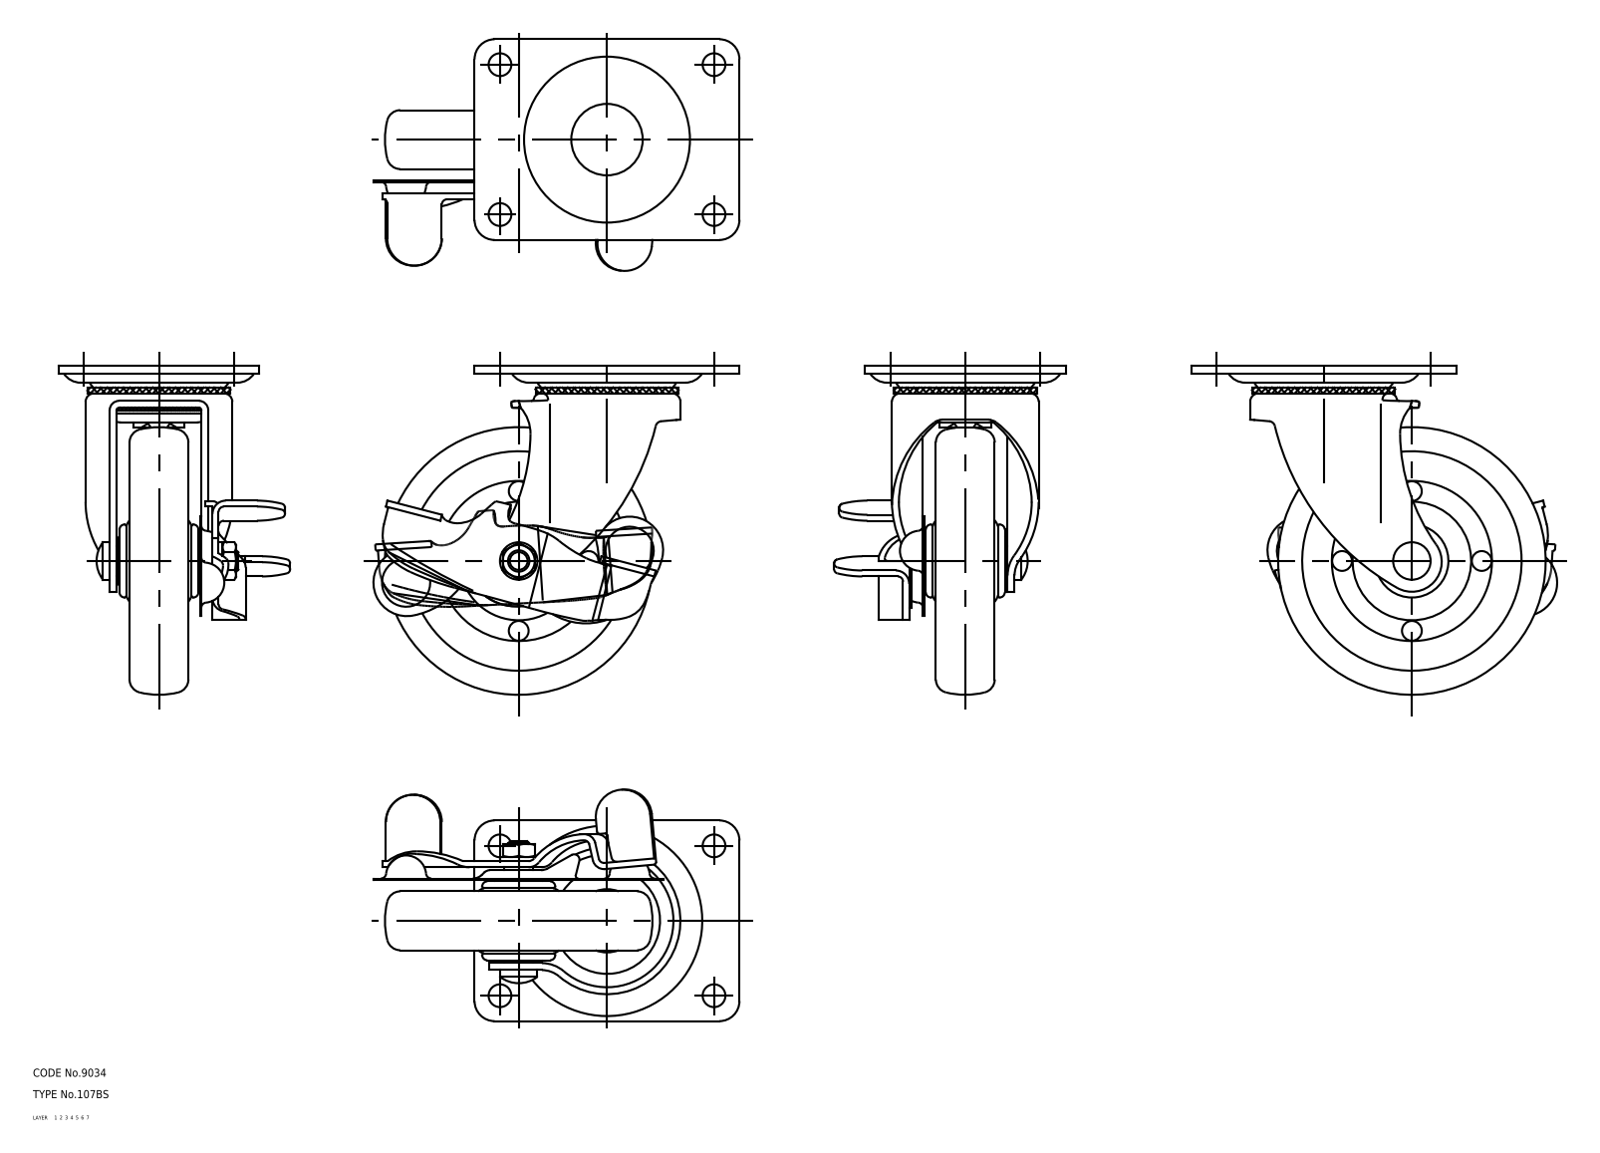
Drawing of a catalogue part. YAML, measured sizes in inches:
part_name: "67136486; 67136499; 67136512; 67136525 (+3 more)"
step_written_by: "CADfix (AUTOMOTIVE_DESIGN)"
units: inches
bodies: {solids: 7, faces: 396, planar: 0, cylindrical: 0, other: 396}
overall_size: [5.385, 4.843, 3.41]
volume: 13.99
surface_area: 123.9
